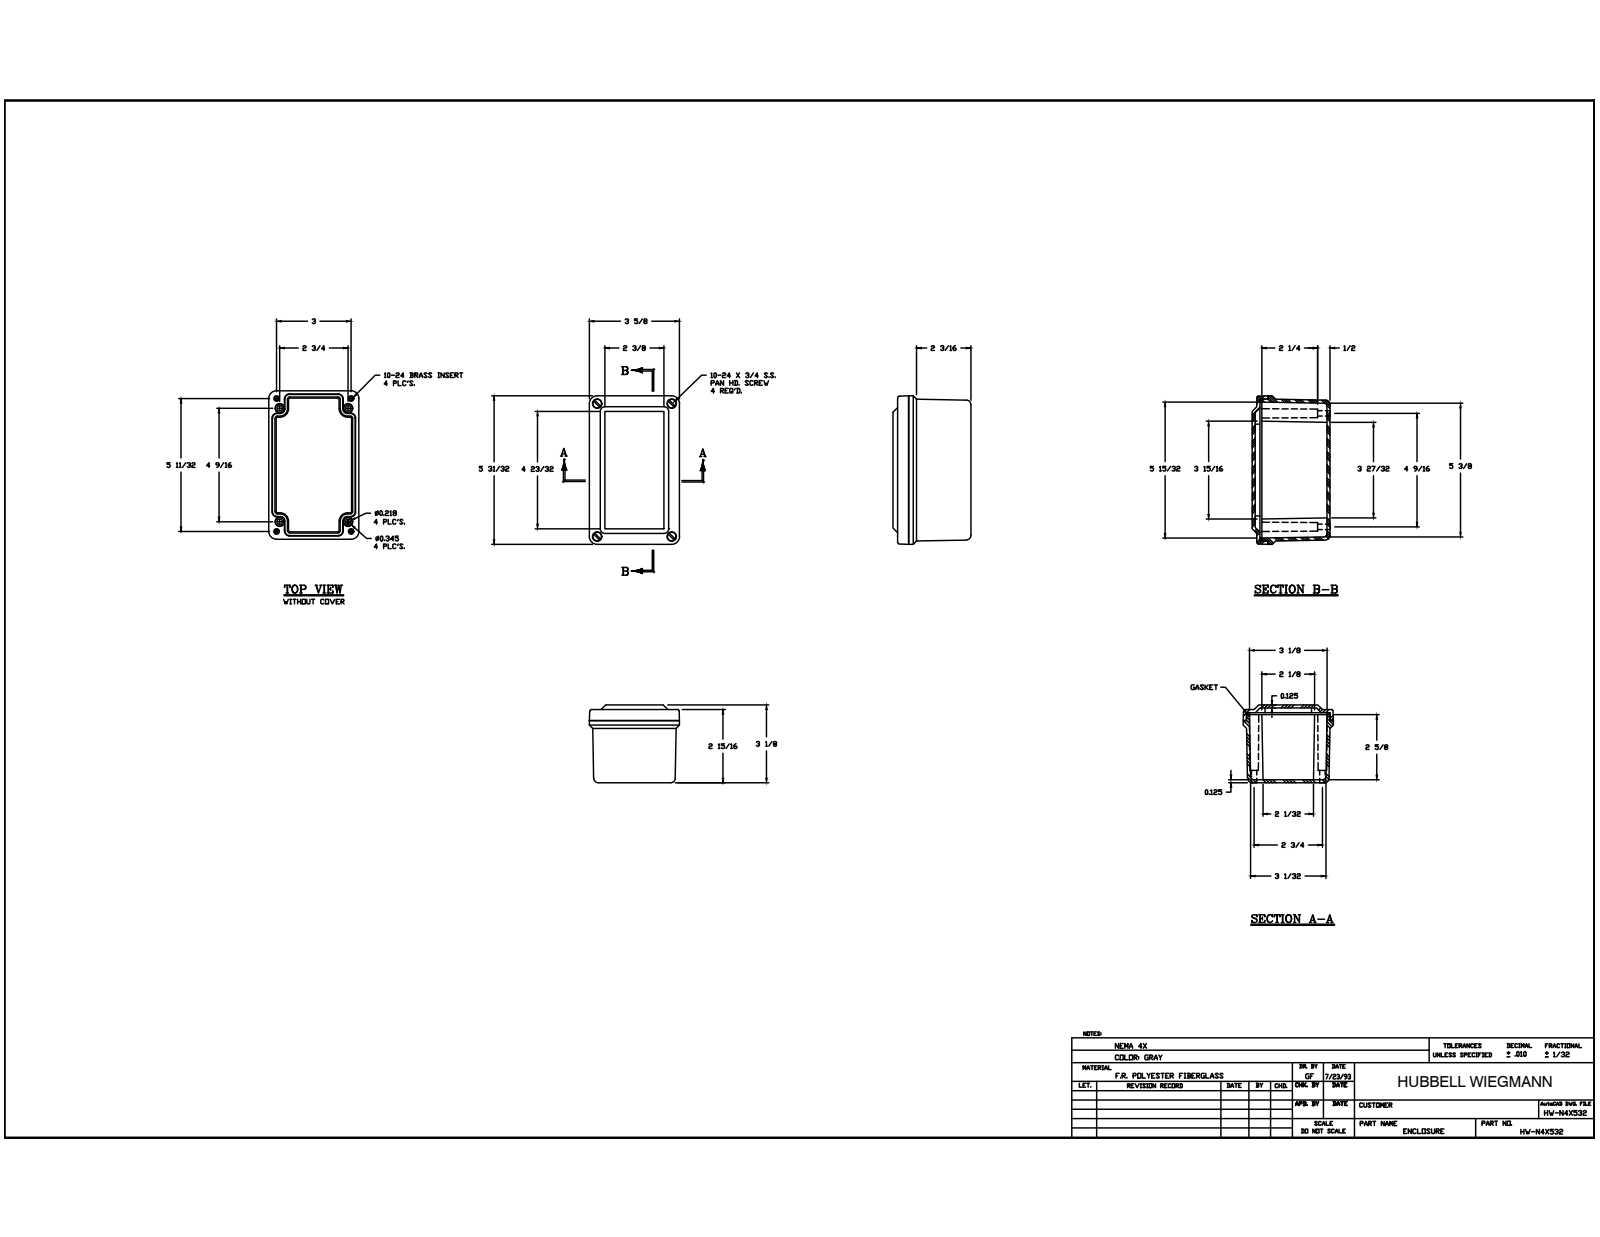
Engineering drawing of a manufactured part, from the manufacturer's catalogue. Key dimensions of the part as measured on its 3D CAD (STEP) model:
Part name (STEP PRODUCT): WPCF532 BOX; 10-24 X 0.4375 DP BRASS INSERT; 10-24x0.75 DP combo screw; WPCF532 GASKET (+3 more)
STEP written by: Autodesk Inventor 2014 (AUTOMOTIVE_DESIGN)
Units: millimetres
Bodies: 11 solids, 375 faces (167 planar, 112 cylindrical, 96 other)
Overall size (bounding box): 151.67 × 92.08 × 79.38
Volume: 240 354 mm³ · Surface area: 136 160 mm²
Round holes (diameter × count): ⌀5.56 ×8, ⌀3.68 ×4, ⌀4.83 ×4, ⌀9.52 ×4
Round bosses / shafts (diameter × count): ⌀9.42 ×4, ⌀5.54 ×4, ⌀4.5 ×4
Partial cylindrical surfaces — rounded edges, fillets, slot ends (radius × count): R0.79 ×20, R0.3 ×16, R1.22 ×8, R1.59 ×4, R4.47 ×4, R4.76 ×4, R5.59 ×4, R7.94 ×4
Main face-to-face distances: 3.17, 3.09, 76.2, 4.76, 71.44, 79.37, 73.03, 1.59, 12.7, 68.27
Hole centre spacings: 10.43, 73.69, 125.85, 145.47, 69.84, 76.2, 115.88, 135.3
